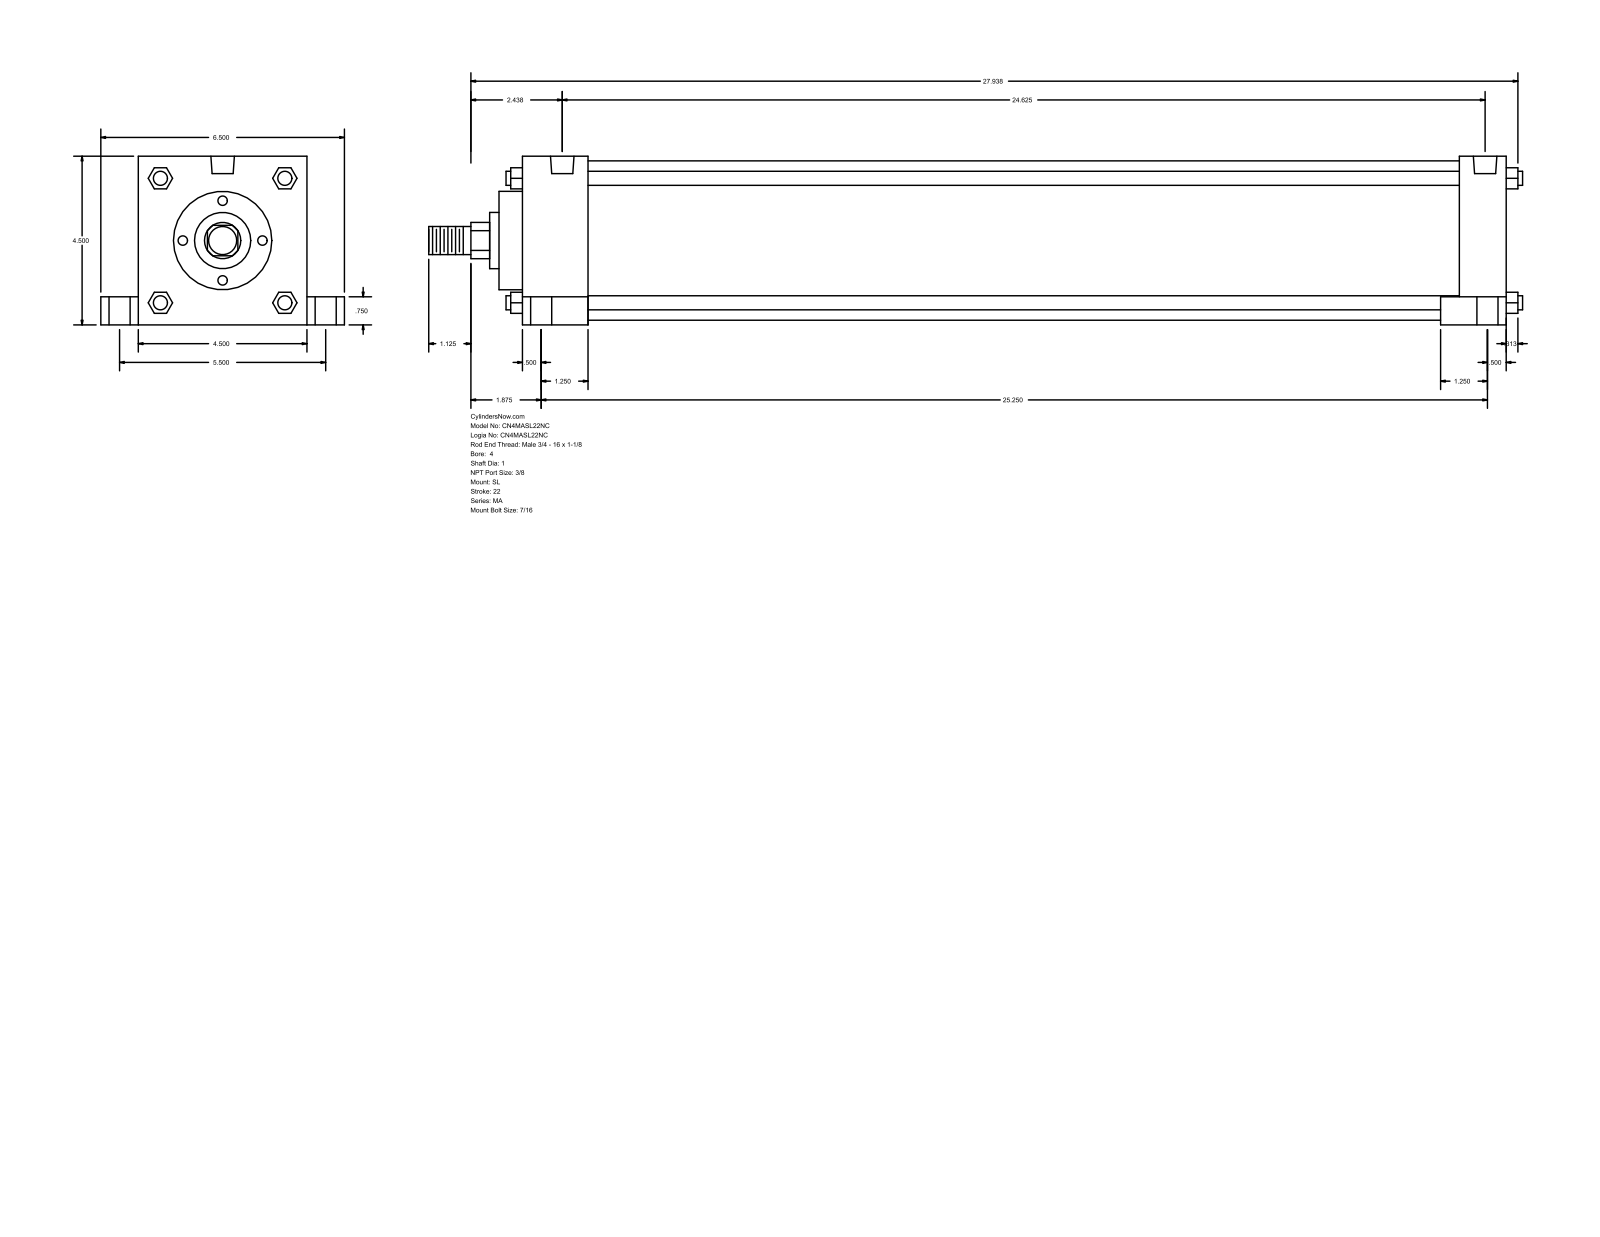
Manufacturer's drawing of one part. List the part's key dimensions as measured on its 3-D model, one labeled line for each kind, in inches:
Part name (STEP PRODUCT): MA_SL__0400_1
STEP written by: GSSL Pune (CONFIG_CONTROL_DESIGN)
Units: inches
Bodies: 0 solids, 150 faces (113 planar, 37 cylindrical, 0 other)
Overall size (bounding box): 29.187 × 6.5 × 4.5
Round holes (diameter × count): ⌀0.437 ×4, ⌀0.563 ×4, ⌀0.813 ×4, ⌀0.627 ×2
Round bosses / shafts (diameter × count): ⌀0.375 ×4, ⌀4.25 ×1, ⌀2.625 ×1, ⌀1.5 ×1, ⌀1 ×1, ⌀0.75 ×1
Partial cylindrical surfaces — rounded edges, fillets, slot ends (radius × count): R0.484 ×1
Main face-to-face distances: 4.5, 26.25, 1.75, 24.5, 25, 23.25, 1.25, 1, 5.5, 26.875
Hole centre spacings: 2.751, 2.761, 2.807, 2.85, 5.5, 24.25, 24.654, 24.841
